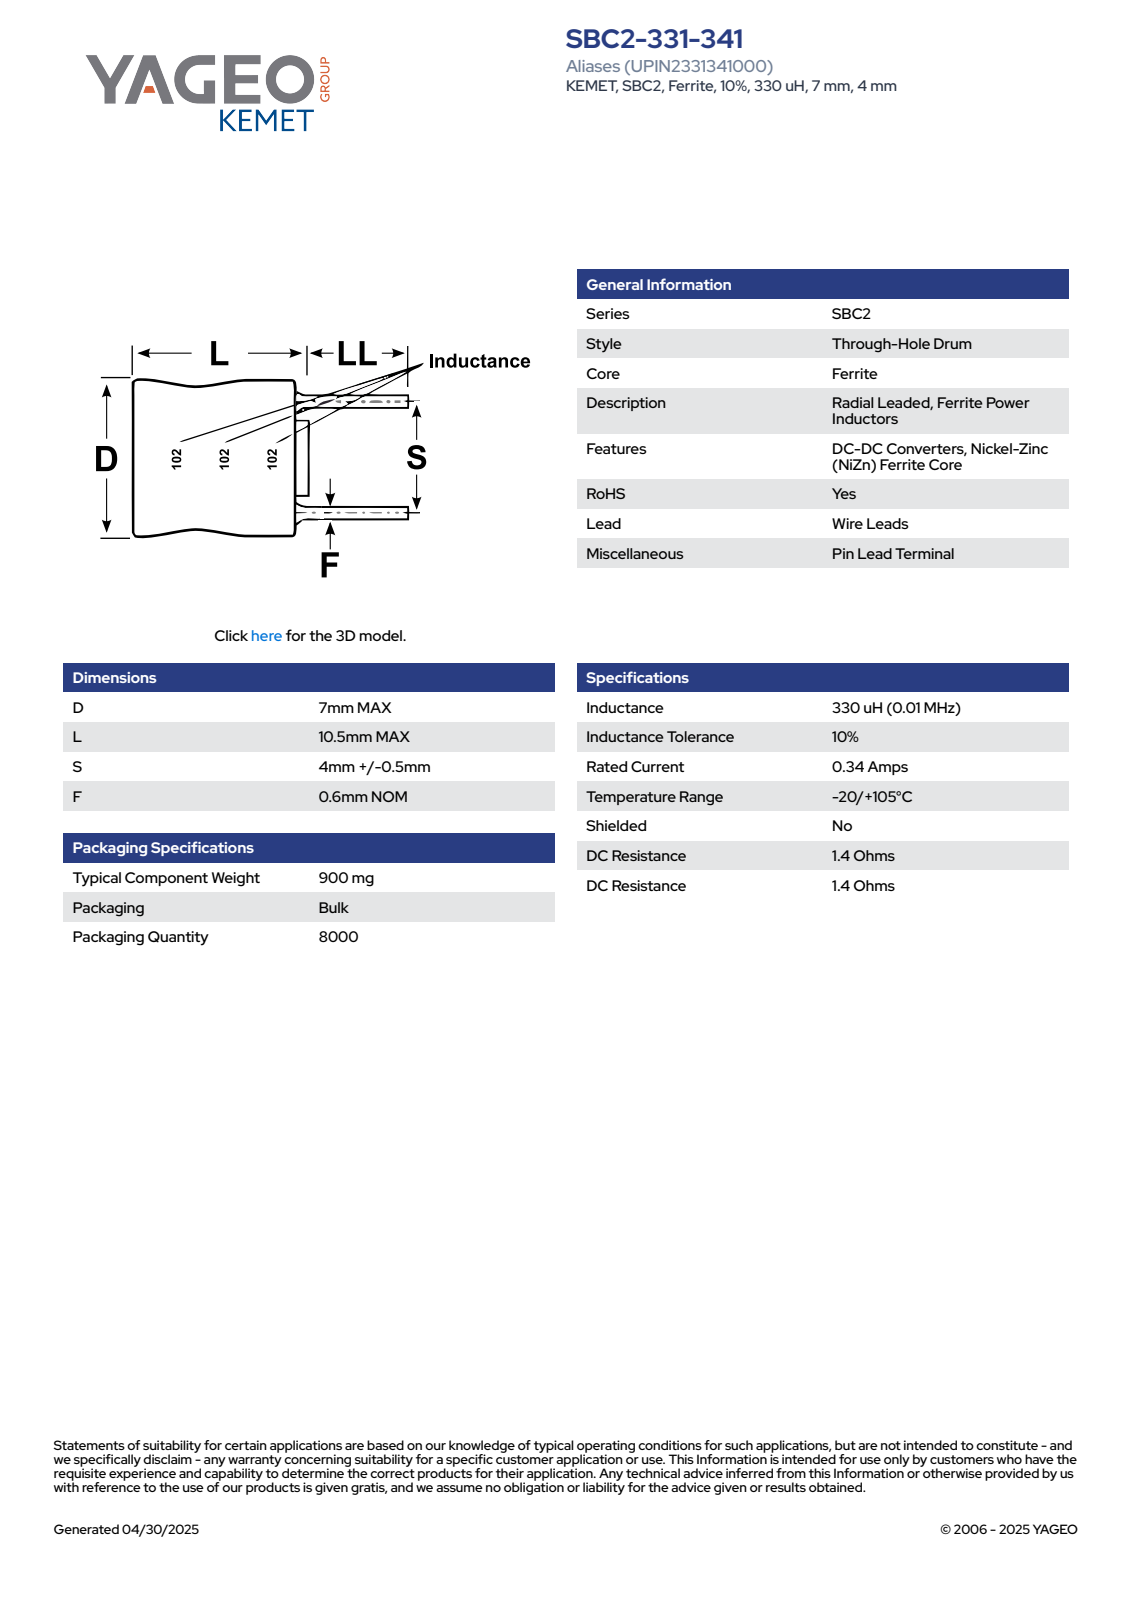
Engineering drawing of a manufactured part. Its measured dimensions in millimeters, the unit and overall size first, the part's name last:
Units: millimetres
Overall size (bounding box): 17 × 7 × 7
Round bosses / shafts (diameter × count): ⌀0.6 ×2, ⌀7 ×1, ⌀6.37 ×1
Main face-to-face distances: 10.19, 10.2, 0.31, 10.5, 10.51, 6.5, 6.81, 17, 17.01, 2.66
Volume: 355 mm³ · Surface area: 319 mm²
Bodies: 4 solids, 84 faces (66 planar, 10 cylindrical, 8 other)
Part name (STEP PRODUCT): IL_SBCP_D7L10.5S4LL6.5F0.6
STEP written by: SolidWorks 2014 (AUTOMOTIVE_DESIGN)
